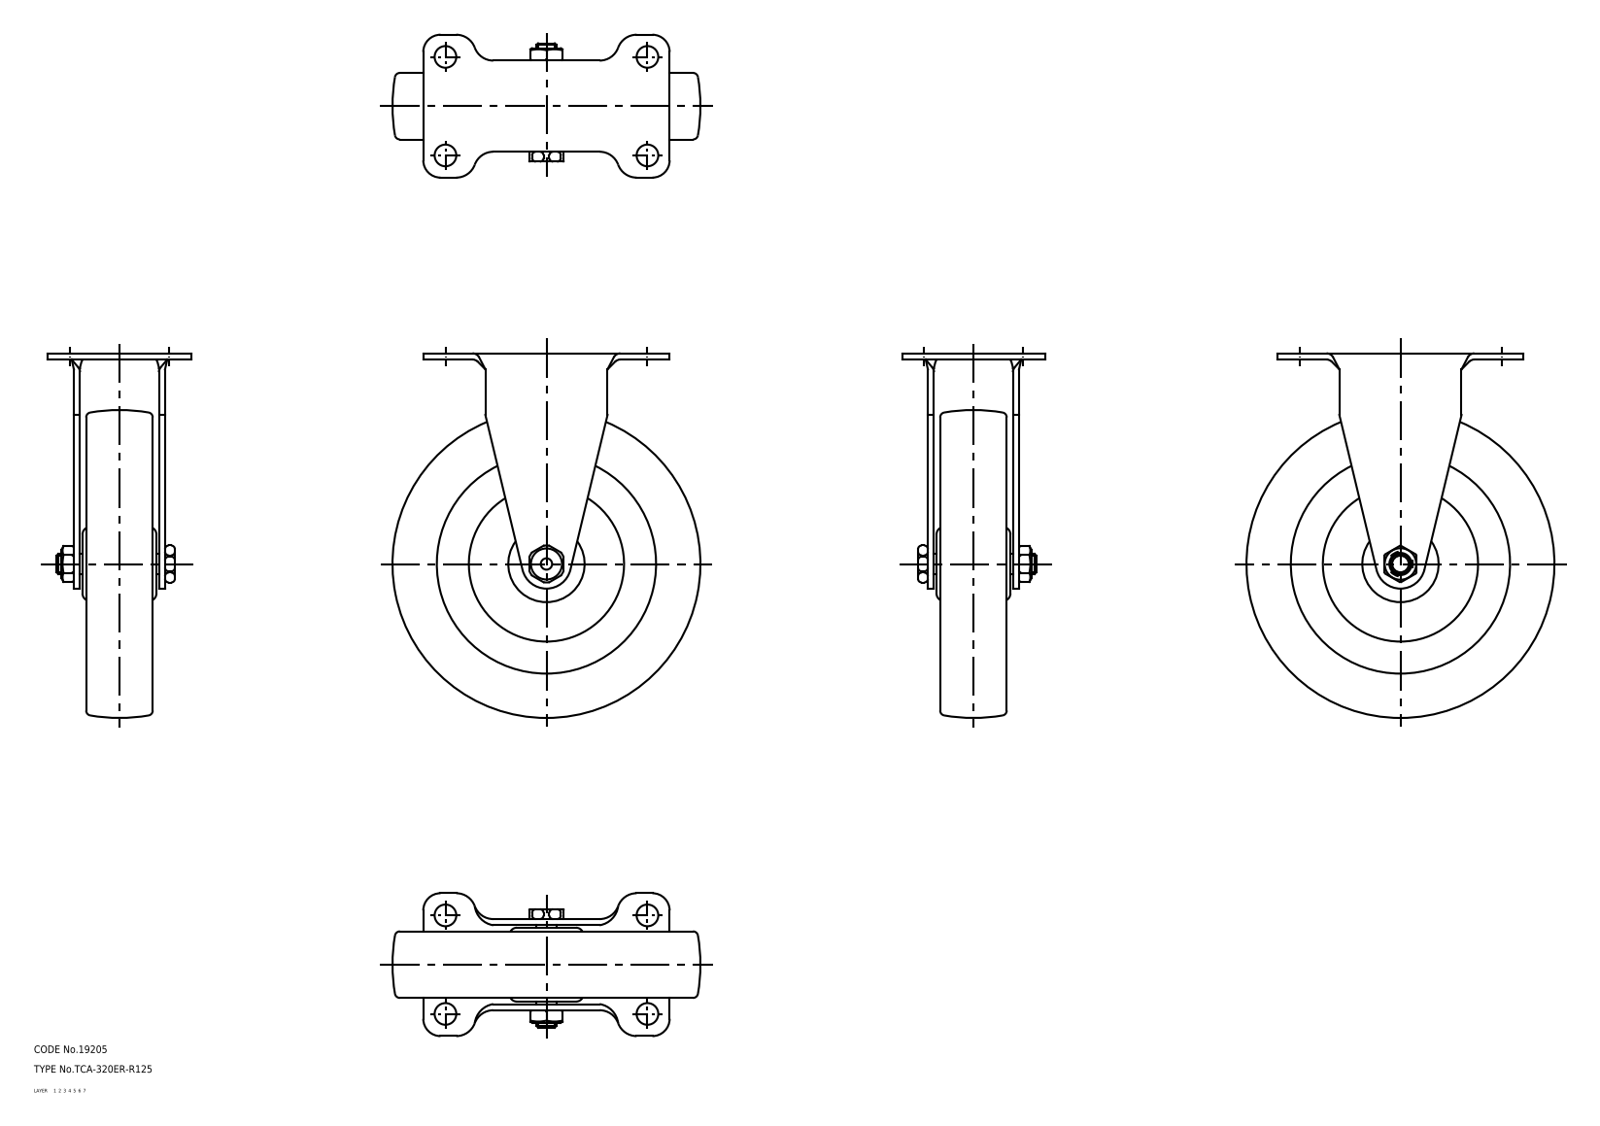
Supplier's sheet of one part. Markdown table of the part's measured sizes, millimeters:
| quantity | value |
| --- | --- |
| part name | wheel; axle; 320ER_R125_3247_36 |
| STEP written by | CADfix (AUTOMOTIVE_DESIGN) |
| units | millimeters |
| bodies | 3 solids, 161 faces (0 planar, 0 cylindrical, 161 other) |
| overall size | 148 × 125 × 58 |
| volume | 337 191 mm³ |
| surface area | 61 063 mm² |
